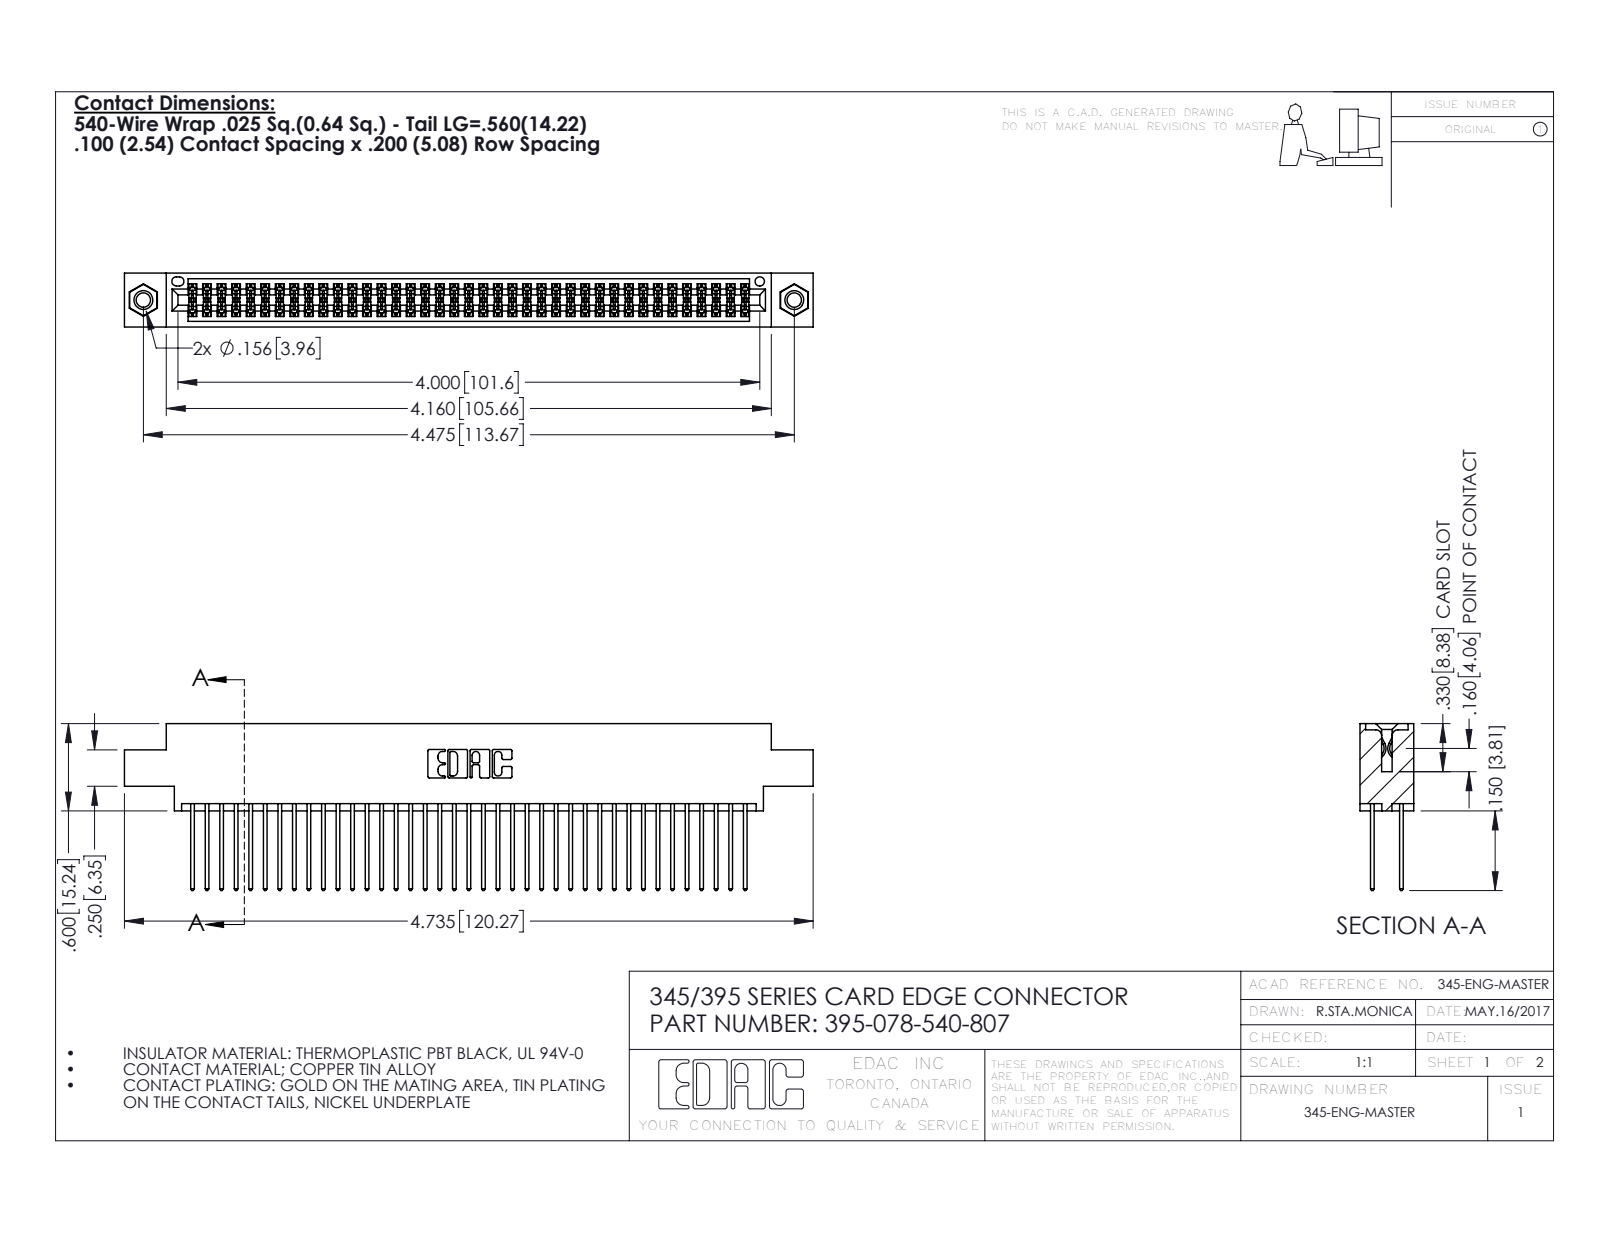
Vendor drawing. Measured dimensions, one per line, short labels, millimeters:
name: 345-250-001_345-250-005-103; 345-292-001_345-293-140; 395-078-540-807; 345 Part_0.170 Offset - 0.156 Dia-TI
written by: SolidWorks 2016 (CONFIG_CONTROL_DESIGN)
unit: mm
bodies: 81 solids, 4090 faces (2690 planar, 1384 cylindrical, 16 other)
size: 120.3 × 29.1 × 9.4
volume: 11 800 mm³; area: 18 960 mm²
holes: 2× ⌀2.5, 2× ⌀3.2, 2× ⌀4, 1× ⌀1.6
bosses: 2× ⌀3.9
rounds: 117× R0.2, 78× R0.3, 22× R0.3, 6× R0.2, 6× R0.8, 3× R0.7, 2× R0.4, 2× R0.5
face distances: 1.8, 7.6, 5.1, 2.5, 6.9, 0.6, 9.4, 5.7, 4.4, 3.8
hole spacings: 6.9, 107.7, 113.7
